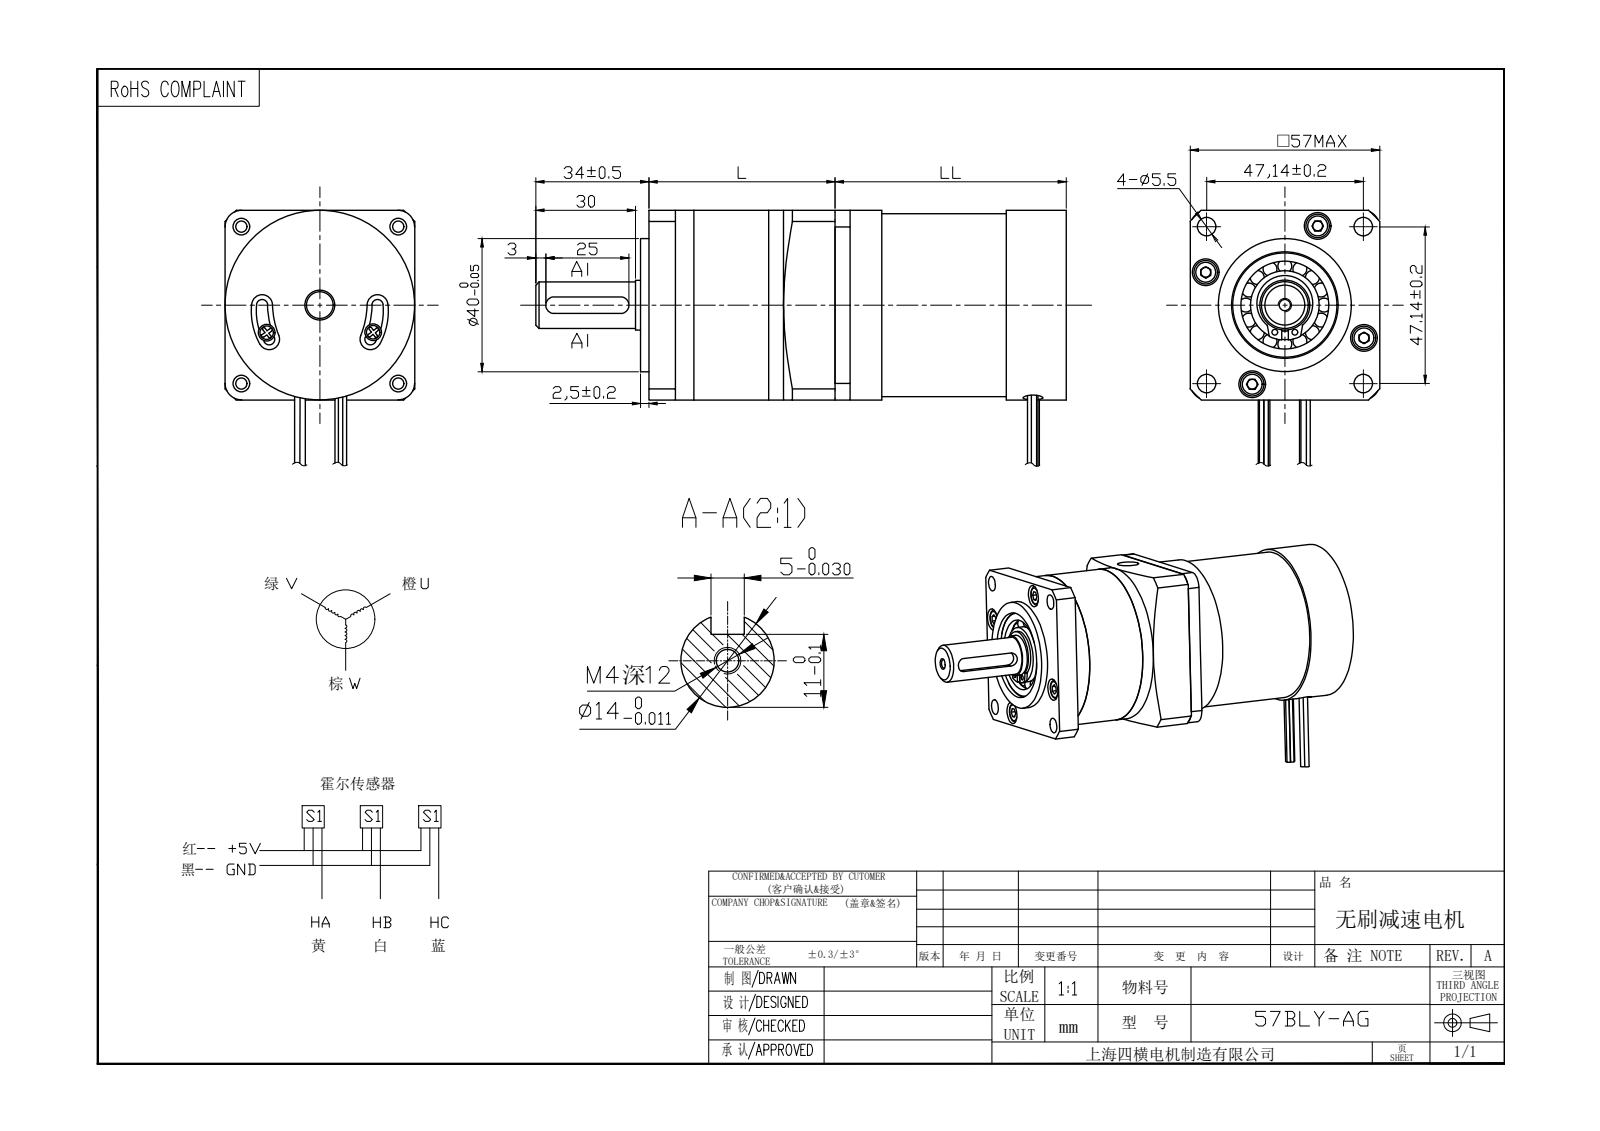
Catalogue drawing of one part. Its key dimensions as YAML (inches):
part_name: "FL前端盖; 57H276A-8-20轴; FL出轴; FL机身 (+8 more)"
step_written_by: "SolidWorks 2020 (AUTOMOTIVE_DESIGN)"
units: inches
bodies: {solids: 32, faces: 749, planar: 277, cylindrical: 288, other: 184}
overall_size: [6.28, 3.248, 2.244]
volume: 18.15
surface_area: 130.7
round_holes:
  - {diameter: 0.315, count: 7}
  - {diameter: 0.197, count: 6}
  - {diameter: 0.13, count: 5}
  - {diameter: 0.217, count: 5}
  - {diameter: 0.177, count: 4}
  - {diameter: 0.118, count: 3}
  - {diameter: 0.067, count: 2}
  - {diameter: 0.098, count: 2}
  - {diameter: 0.236, count: 2}
  - {diameter: 0.256, count: 2}
  - {diameter: 0.354, count: 1}
  - {diameter: 0.543, count: 1}
round_bosses_or_shafts:
  - {diameter: 0.197, count: 5}
  - {diameter: 0.051, count: 5}
  - {diameter: 0.276, count: 4}
  - {diameter: 0.157, count: 4}
  - {diameter: 0.063, count: 3}
  - {diameter: 0.118, count: 2}
  - {diameter: 2.244, count: 1}
  - {diameter: 2.165, count: 1}
partial_cylinders:
  - {radius: 0.016, count: 10}
  - {radius: 0.017, count: 10}
  - {radius: 0.065, count: 4}
  - {radius: 0.124, count: 4}
  - {radius: 0.197, count: 4}
  - {radius: 0.008, count: 2}
  - {radius: 0.02, count: 2}
  - {radius: 0.098, count: 2}
face_to_face_distances: [0.551, 0.886, 1.339, 2.224, 2.028, 0.787, 1.673, 2.244, 2.185, 1.476]
hole_center_spacings: [1.312, 1.856, 1.856, 2.282, 0.54, 1.316, 0.443, 0.93]
